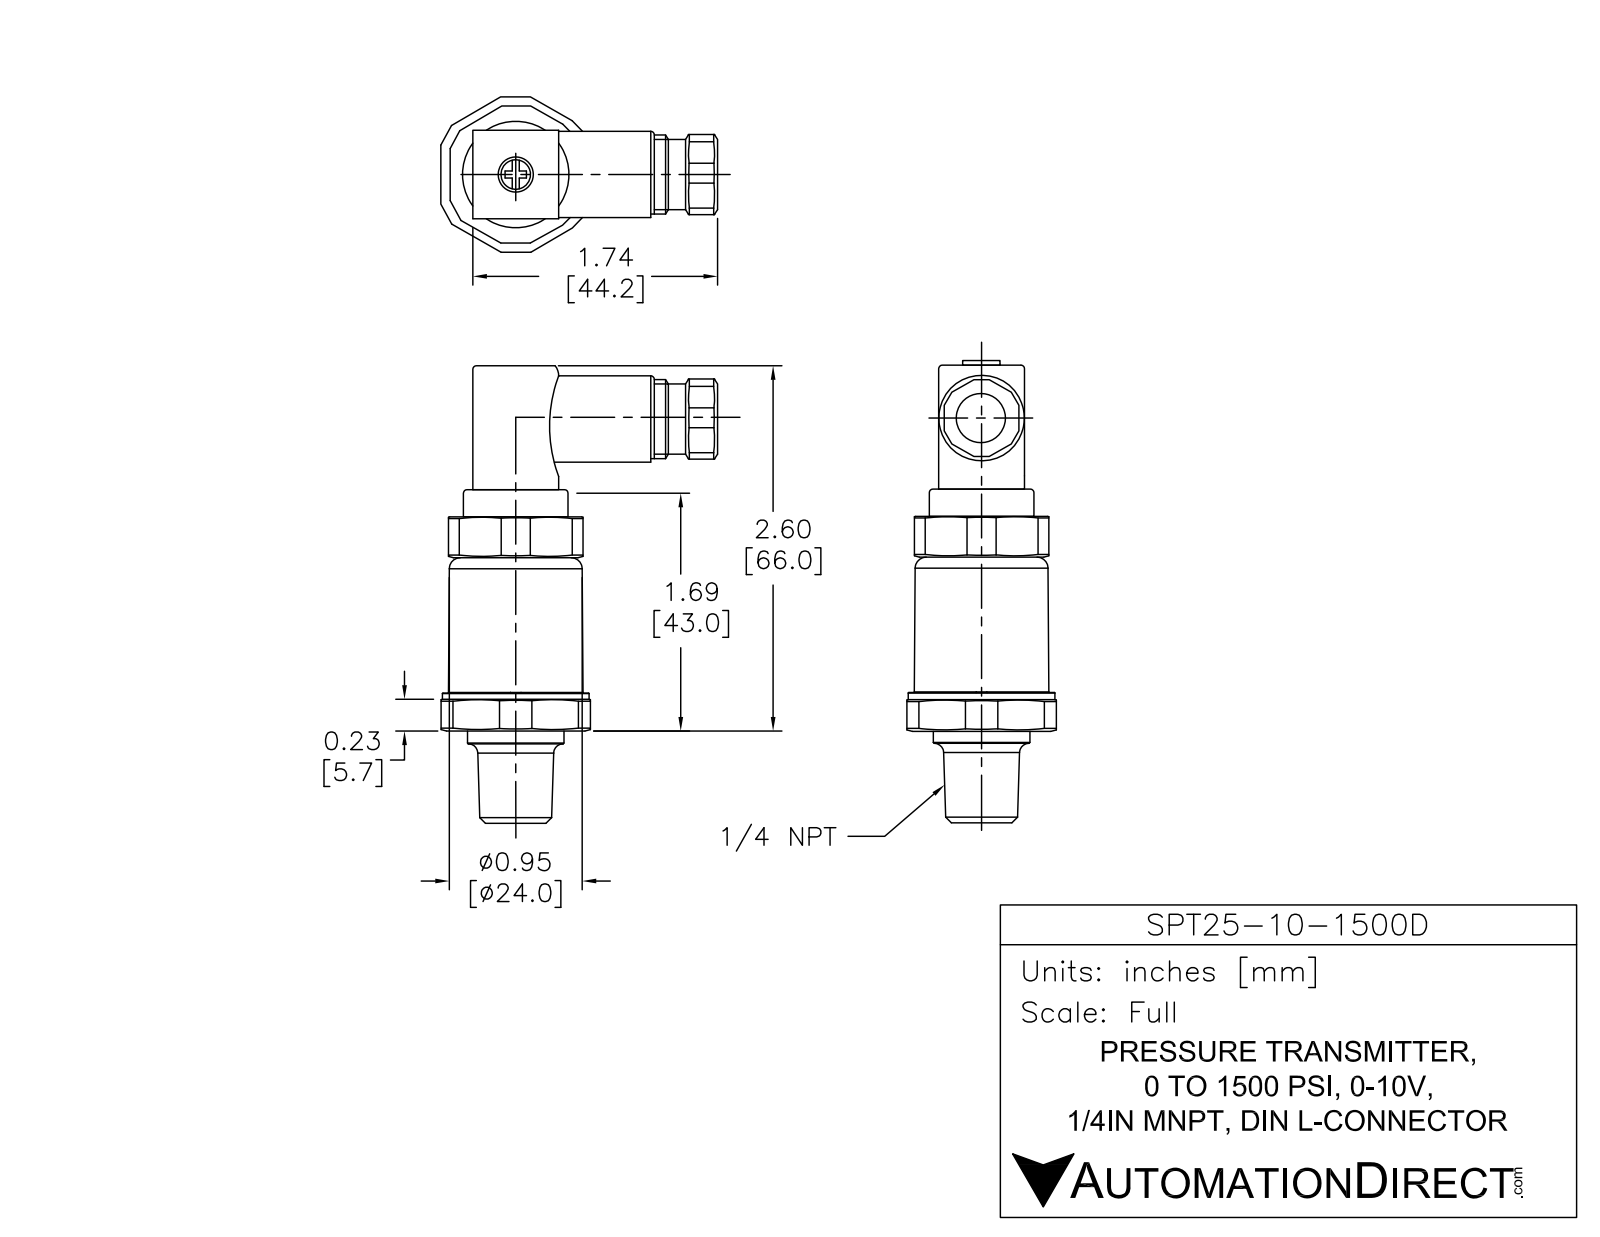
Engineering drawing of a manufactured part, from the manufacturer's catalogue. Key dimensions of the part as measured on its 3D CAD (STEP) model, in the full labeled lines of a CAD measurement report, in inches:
Part name (STEP PRODUCT): SPT25-10-1500D
STEP written by: SolidWorks 2011 (AUTOMOTIVE_DESIGN)
Units: inches
Bodies: 5 solids, 170 faces (96 planar, 64 cylindrical, 10 other)
Overall size (bounding box): 3.199 × 1.496 × 1.406
Volume: 1.703 in³ · Surface area: 15.71 in²
Round holes (diameter × count): ⌀0.039 ×1, ⌀0.13 ×1, ⌀0.276 ×1, ⌀0.315 ×1
Round bosses / shafts (diameter × count): ⌀1.053 ×1, ⌀0.945 ×1, ⌀0.689 ×1, ⌀0.591 ×1, ⌀0.551 ×1, ⌀0.433 ×1
Partial cylindrical surfaces — rounded edges, fillets, slot ends (radius × count): R0.059 ×8, R0.045 ×4, R0.089 ×4, R0.079 ×3, R0.045 ×1, R0.046 ×1, R0.571 ×1
Main face-to-face distances: 0.059, 1.161, 1.22, 0.62, 0.014, 0.606, 0.266, 1.486, 1.427, 0.197
Hole centre spacings: 0.052
